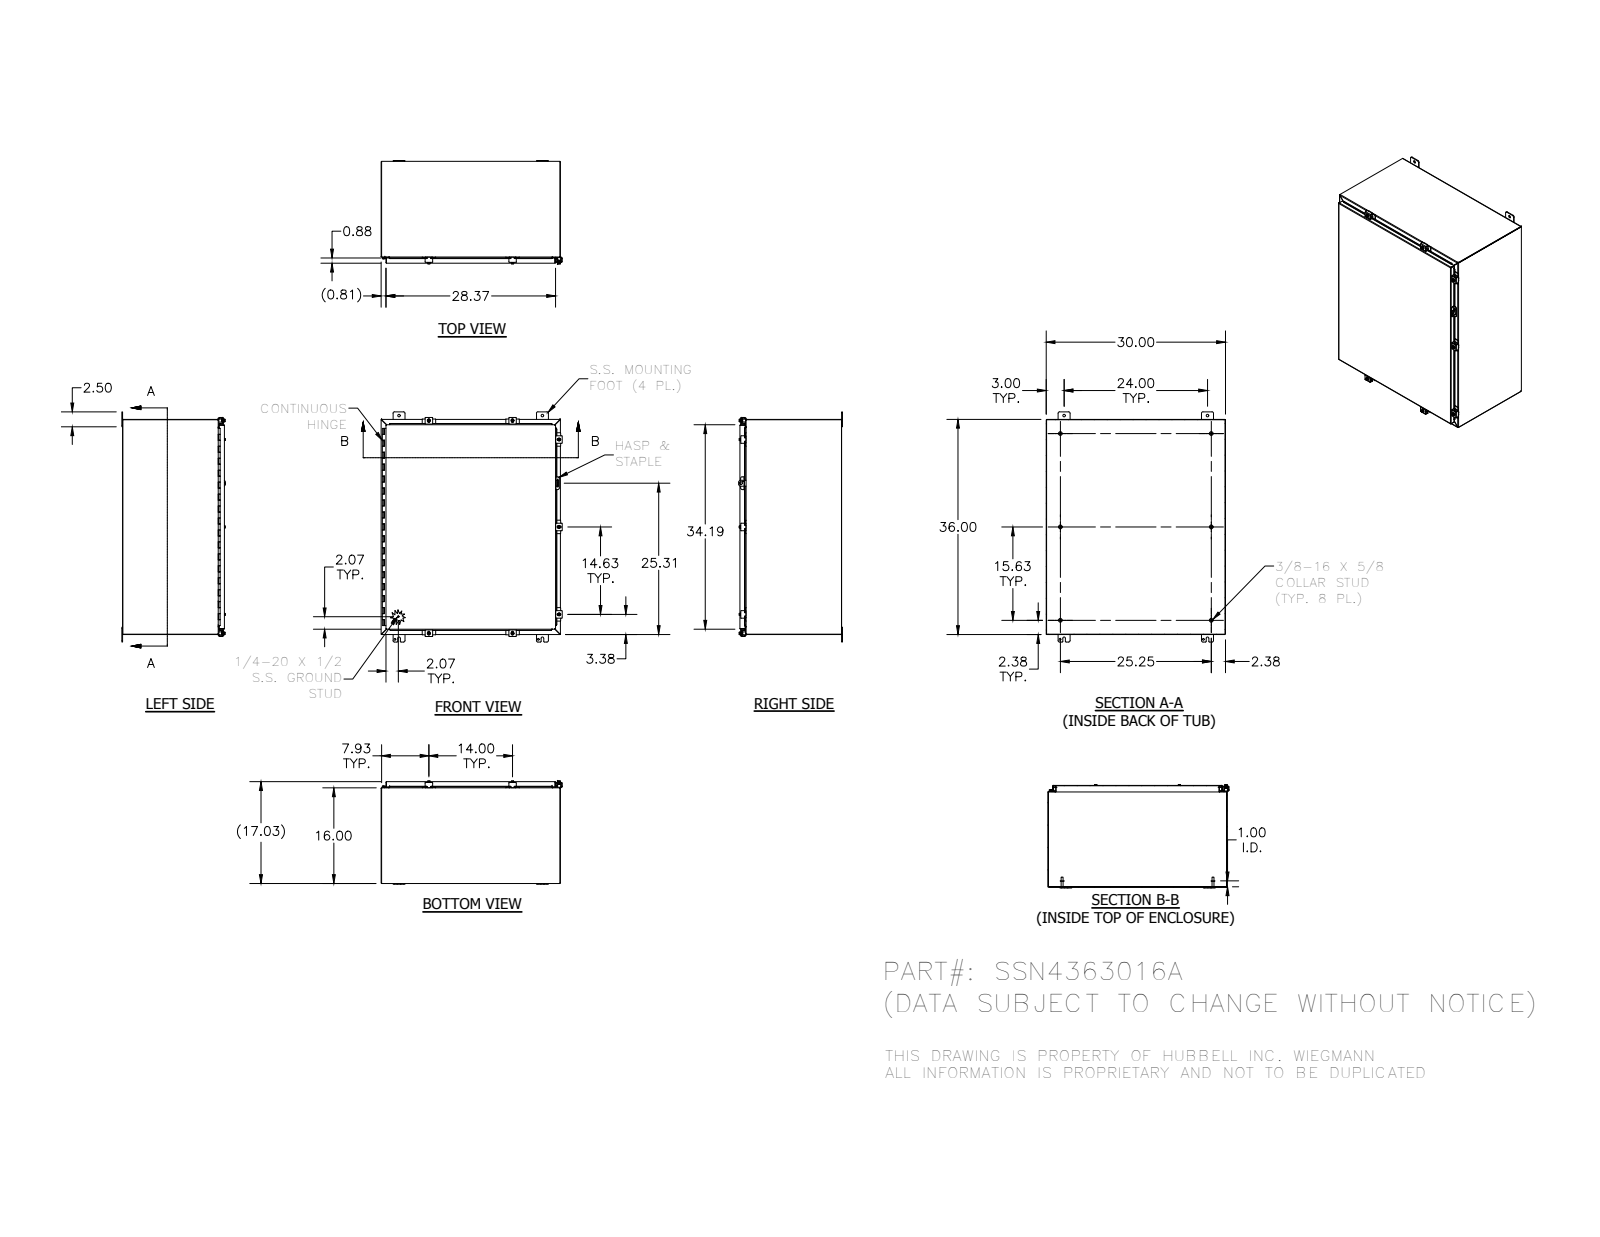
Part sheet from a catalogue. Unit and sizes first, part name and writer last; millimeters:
Units: millimetres
Overall size (bounding box): 977.9 × 769.9 × 440.8
Round holes (diameter × count): ⌀5.4 ×7, ⌀7.1 ×7, ⌀7.6 ×7, ⌀8 ×4, ⌀11.1 ×4, ⌀3.2 ×1, ⌀4 ×1, ⌀12.7 ×1
Round bosses / shafts (diameter × count): ⌀6.4 ×9, ⌀13.2 ×7, ⌀12.7 ×7, ⌀8.9 ×7, ⌀15.9 ×6, ⌀8.4 ×6, ⌀8.6 ×1, ⌀3 ×1
Partial cylindrical surfaces — rounded edges, fillets, slot ends (radius × count): R0.8 ×83, R3.2 ×37, R6.4 ×33, R0.8 ×21, R2.7 ×21, R1.6 ×14, R3.6 ×14, R2.5 ×10
Main face-to-face distances: 1.9, 430.8, 760.1, 428.9, 432.6, 912.5, 758.2, 762, 910.6, 914.4
Hole centre spacings: 214.2, 559.8, 609.6, 40.5, 914.4, 1099, 110.1, 124.1
Volume: 5 908 000 mm³ · Surface area: 6 175 000 mm²
Bodies: 56 solids, 2032 faces (842 planar, 883 cylindrical, 307 other)
Part name (STEP PRODUCT): 32874-36P; SSN4363016ALRS; HFW308001; 38859 (+8 more)
STEP written by: SolidWorks 2014 (AUTOMOTIVE_DESIGN)
